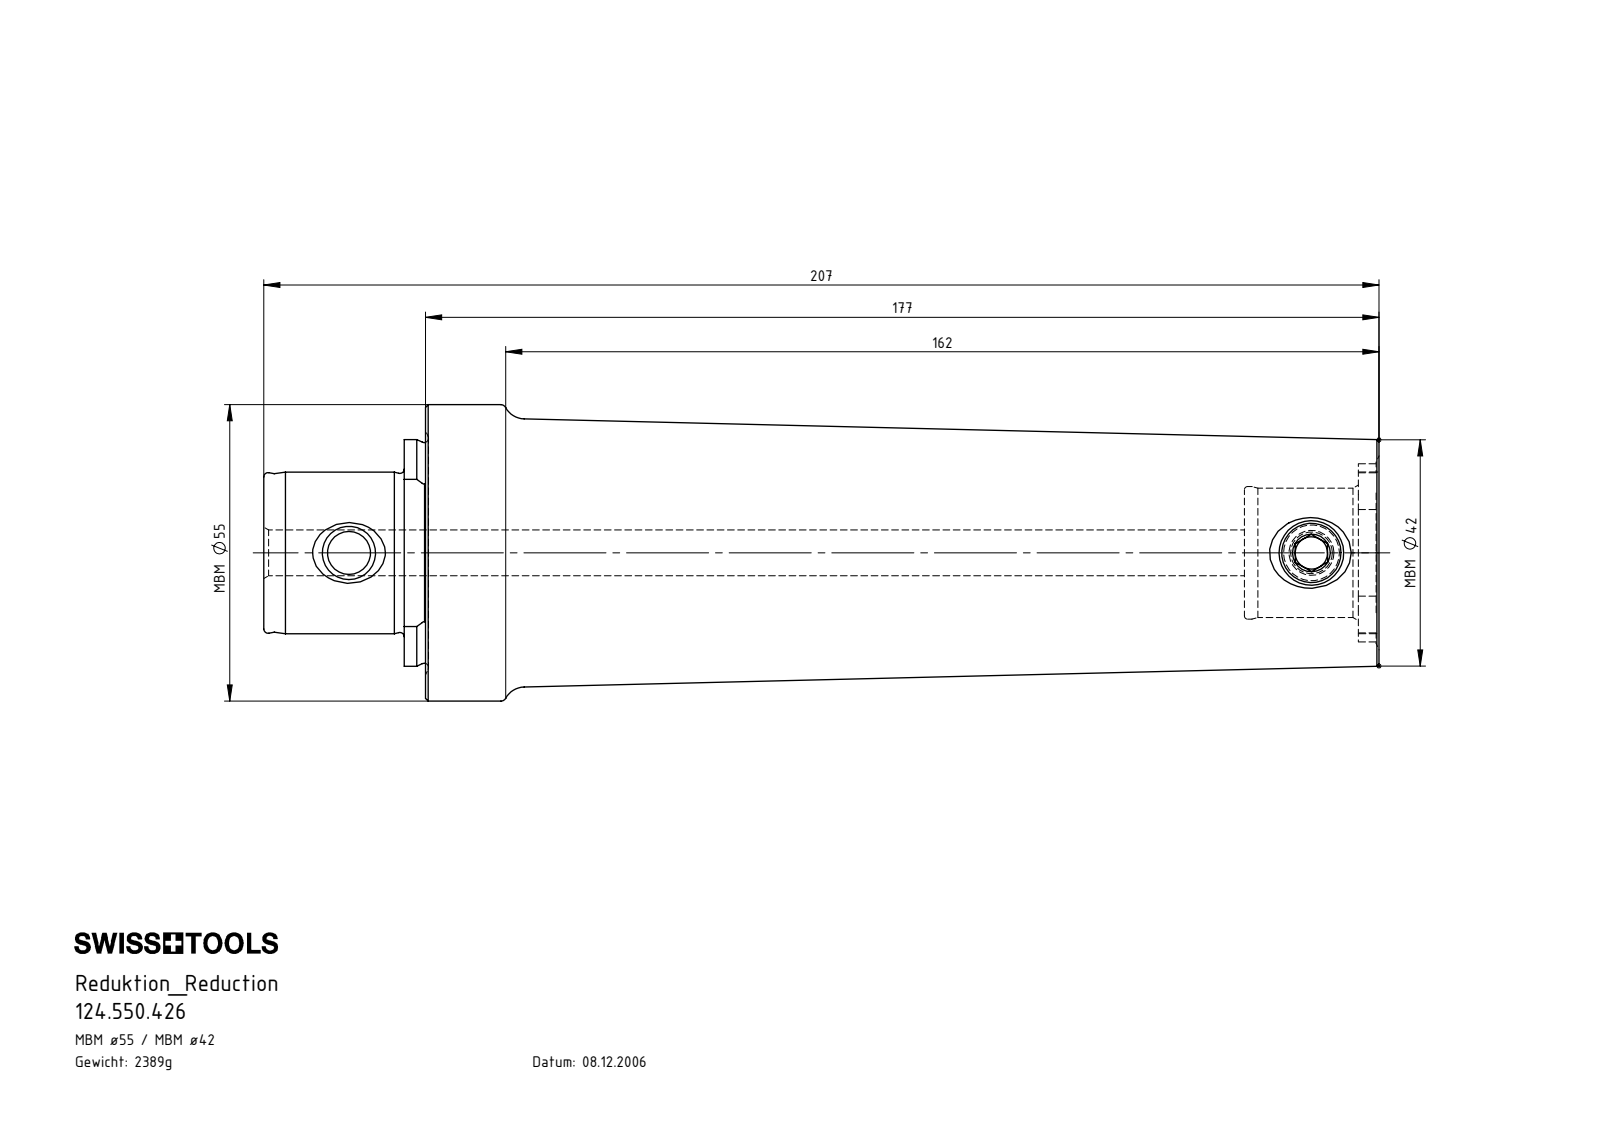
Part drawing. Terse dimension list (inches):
name: MB4-ER1.001.013_A; 124.550.426; MB5-MB4.K01.177_C
written by: SolidWorks 2017 (CONFIG_CONTROL_DESIGN)
unit: in
bodies: 2 solids, 131 faces (32 planar, 32 cylindrical, 67 other)
size: 8.15 × 2.165 × 2.165
volume: 18.57 in³; area: 62.8 in²
holes: 1× ⌀0.236, 1× ⌀0.315, 1× ⌀0.335, 1× ⌀0.433, 1× ⌀0.945, 1× ⌀0.969
bosses: 1× ⌀2.165, 1× ⌀1.181, 1× ⌀0.472
rounds: 4× R0.165, 1× R0.587, 1× R0.65, 1× R0.828
face distances: 1.181, 1.026, 0.156, 7.165, 6.14, 5.984, 7.998, 6.972, 6.817, 0.833
hole spacings: 7.033
